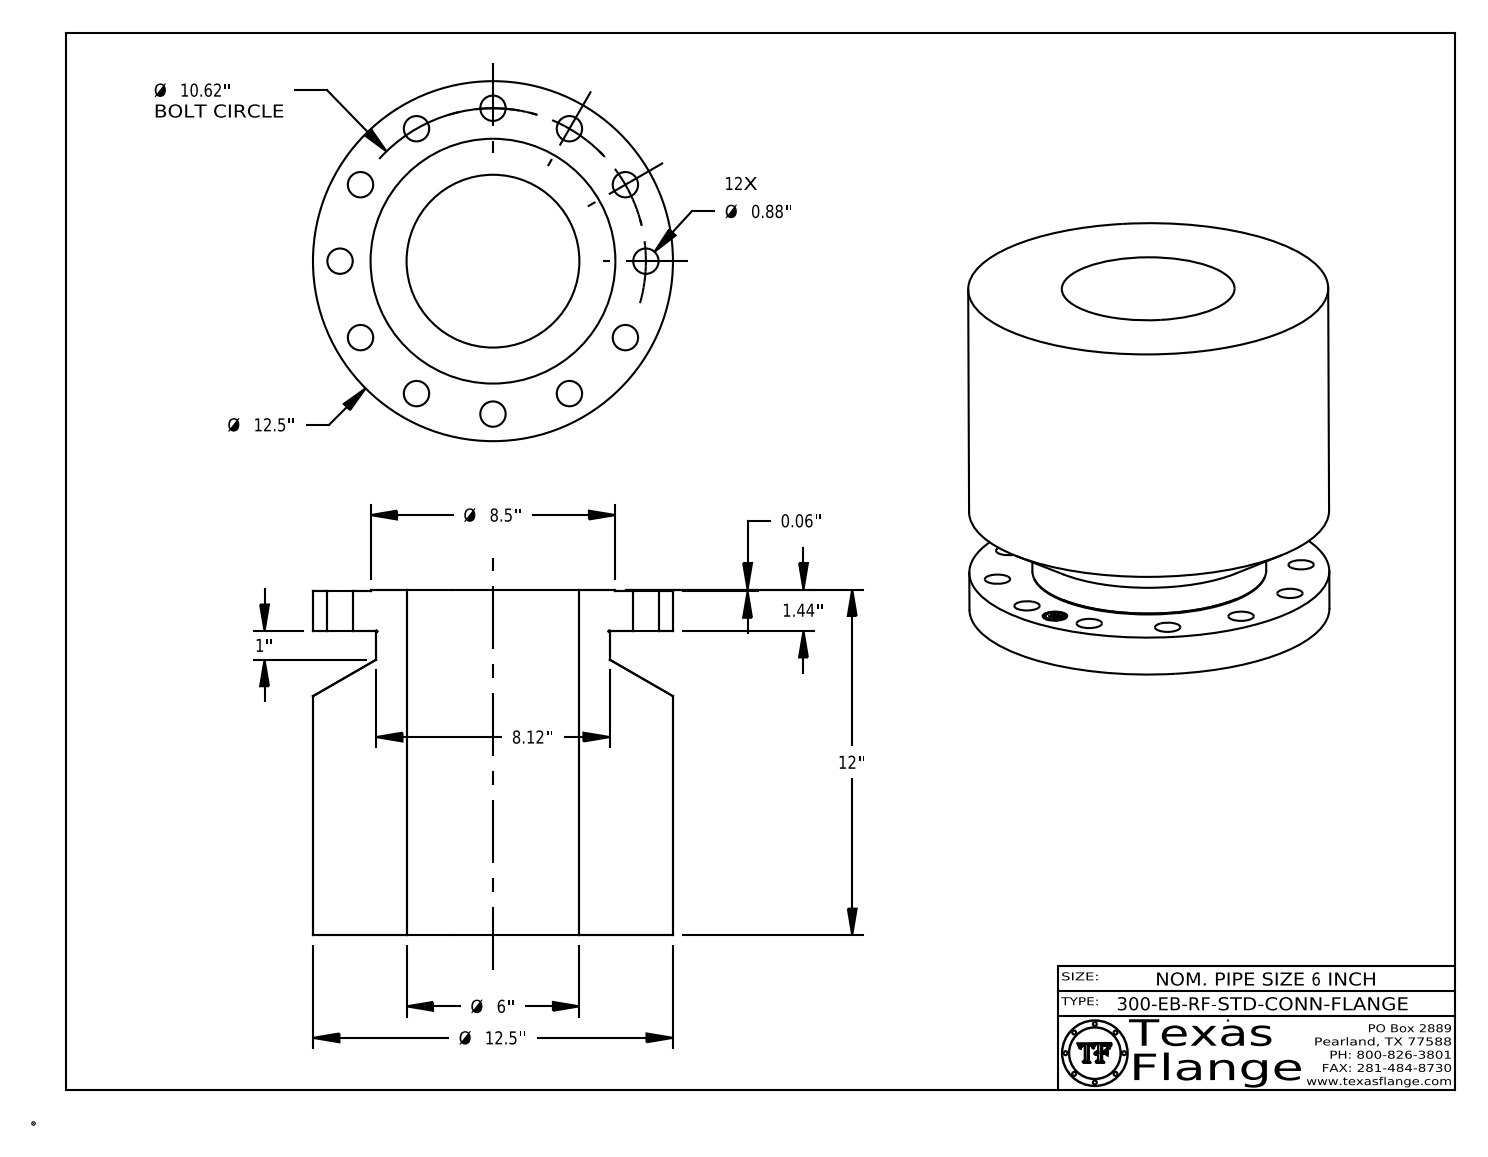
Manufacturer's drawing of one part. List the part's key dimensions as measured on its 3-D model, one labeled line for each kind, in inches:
Part name (STEP PRODUCT): 6-300-EB-RF-STD-CONN-FLANGE
STEP written by: CATIA V5 STEP AP214 (AUTOMOTIVE_DESIGN)
Units: inches
Bodies: 1 solid, 429 faces (369 planar, 54 cylindrical, 6 other)
Overall size (bounding box): 12.5 × 12.5 × 12
Volume: 1 000 in³ · Surface area: 1 007 in²
Round holes (diameter × count): ⌀0.88 ×12, ⌀0.85 ×1, ⌀6 ×1
Round bosses / shafts (diameter × count): ⌀0.051 ×8, ⌀12.5 ×1, ⌀8.5 ×1, ⌀8.12 ×1, ⌀0.67 ×1
Main face-to-face distances: 10.56, 1.378, 11.937, 0.063, 1.44, 12, 1.435, 1.372, 10.565, 0.254
Hole centre spacings: 5.31, 10.258, 2.749, 7.509, 9.197, 10.62, 5.31, 2.748
